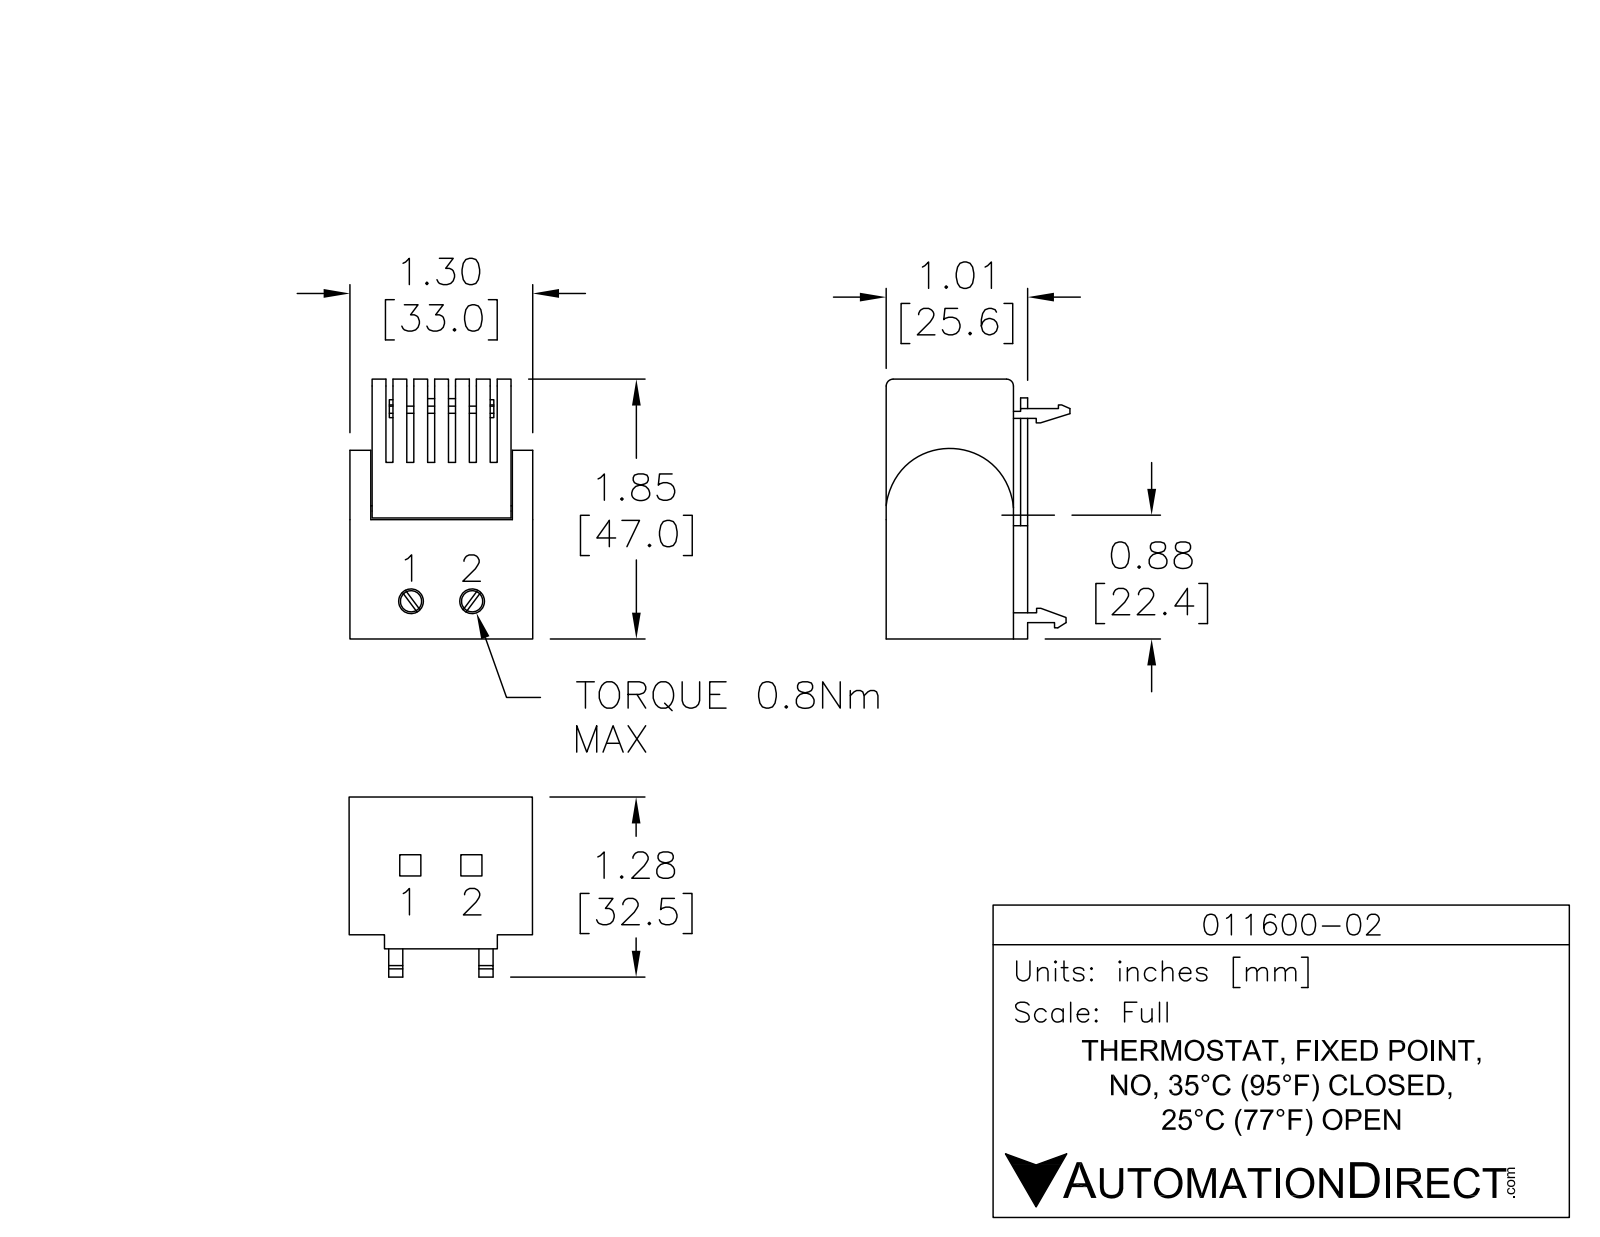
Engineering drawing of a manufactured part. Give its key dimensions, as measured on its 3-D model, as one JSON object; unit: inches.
{"part_name": "011600-02", "step_written_by": "SolidWorks 2013 (AUTOMOTIVE_DESIGN)", "units": "inches", "bodies": {"solids": 1, "faces": 374, "planar": 188, "cylindrical": 123, "other": 63}, "overall_size": [1.821, 1.305, 1.285], "volume_in3": 1.989, "surface_area_in2": 15.56, "partial_cylinders_radius": [[0.025, 16], [0.023, 10], [0.03, 8], [0.015, 7], [0.06, 7], [0.04, 4], [0.026, 3], [0.026, 2]], "face_to_face_distances": [1.305, 0.095, 0.91, 0.911, 0.178, 1.127, 0.14, 0.28, 0.028, 1.821]}
